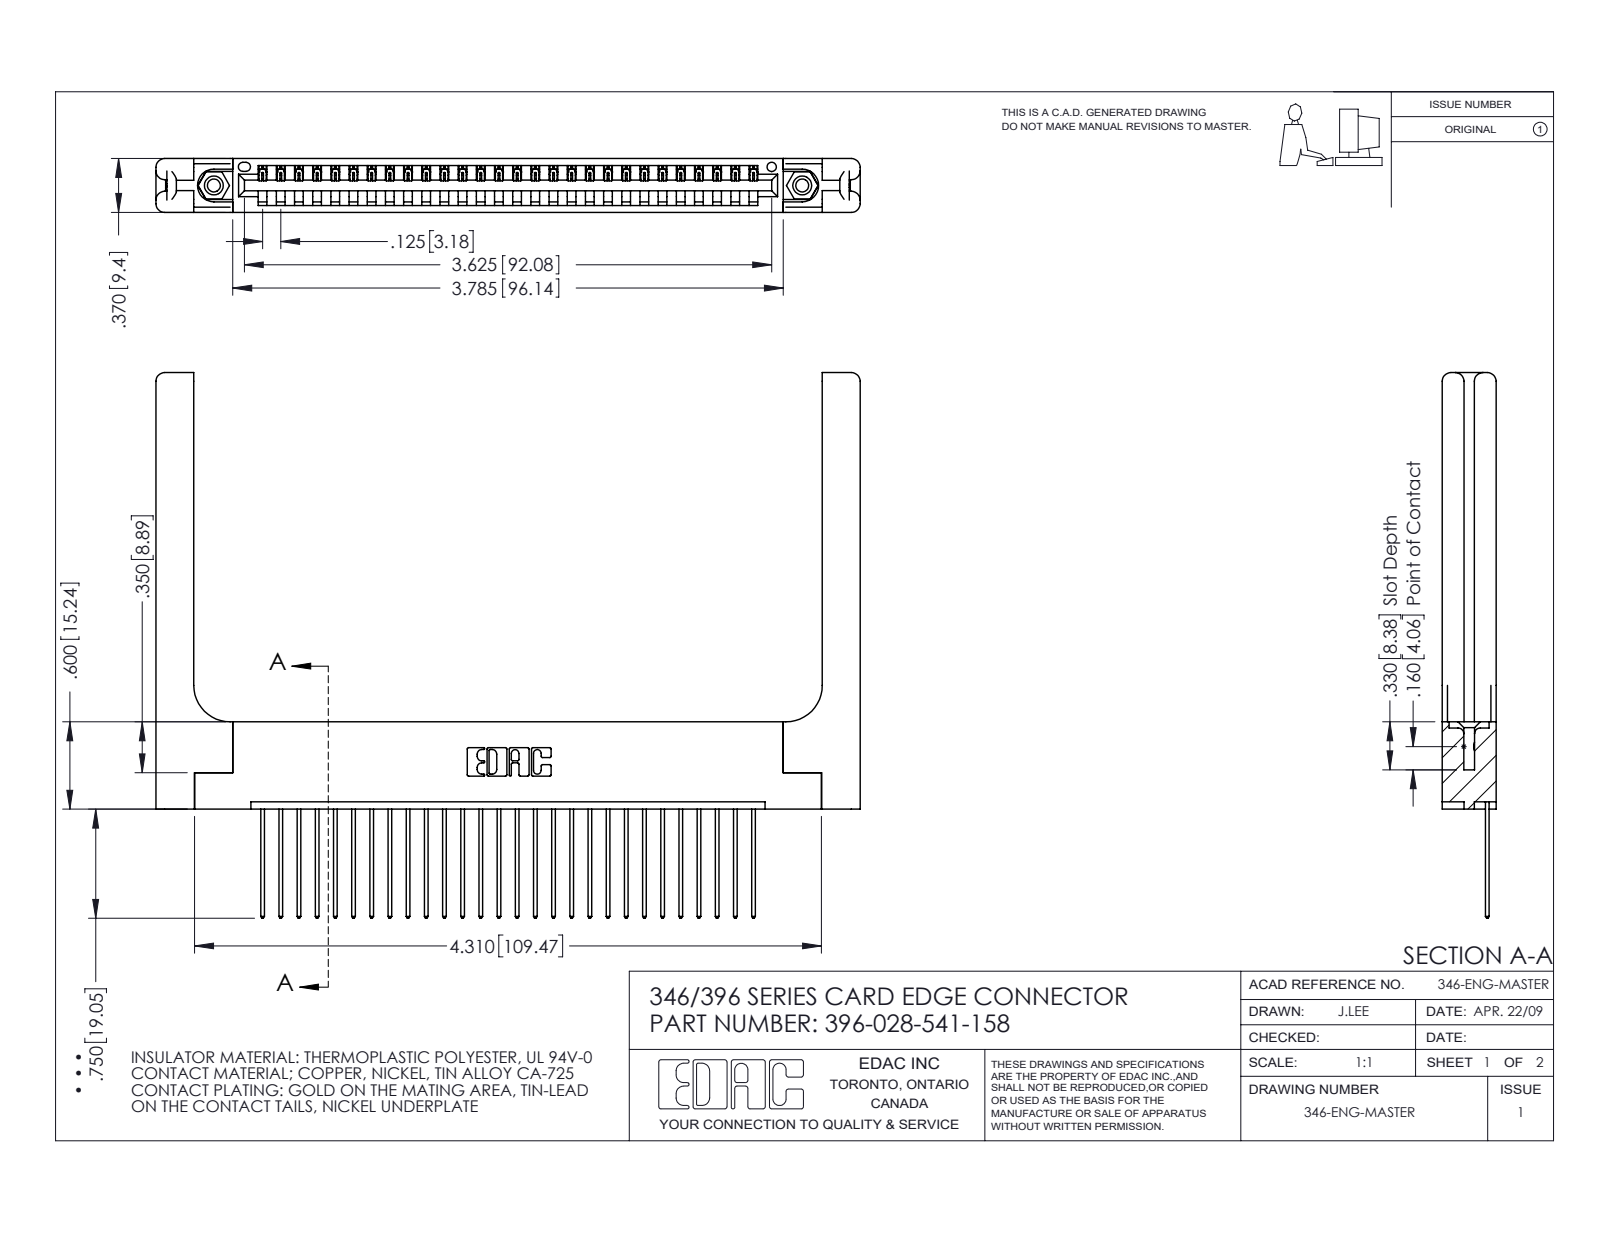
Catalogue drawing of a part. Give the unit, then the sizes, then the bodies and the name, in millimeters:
Units: millimetres
Overall size (bounding box): 123 × 95.3 × 9.4
Round holes (diameter × count): ⌀2.3 ×2, ⌀3.2 ×2, ⌀4 ×2, ⌀1.6 ×1
Round bosses / shafts (diameter × count): ⌀3.9 ×2
Partial cylindrical surfaces — rounded edges, fillets, slot ends (radius × count): R0.2 ×56, R0.3 ×56, R0.3 ×22, R1.5 ×16, R0.2 ×6, R0.8 ×6, R0.7 ×3, R0.8 ×2
Main face-to-face distances: 9.4, 1.8, 1.2, 8.2, 3.8, 3.8, 6.4, 7.6, 0.6, 1.9
Hole centre spacings: 6.2, 97.5, 102.7
Volume: 19 290 mm³ · Surface area: 20 280 mm²
Bodies: 33 solids, 2002 faces (1344 planar, 598 cylindrical, 60 other)
Part name (STEP PRODUCT): 345-250-001_345-250-001-102; 345-292-001_345-293-141; 346 Part_Flush Mounting Lugs - 0.156 Dia-TH; 346-220-058_345-220-058 (+1 more)
STEP written by: SolidWorks 2016 (CONFIG_CONTROL_DESIGN)
